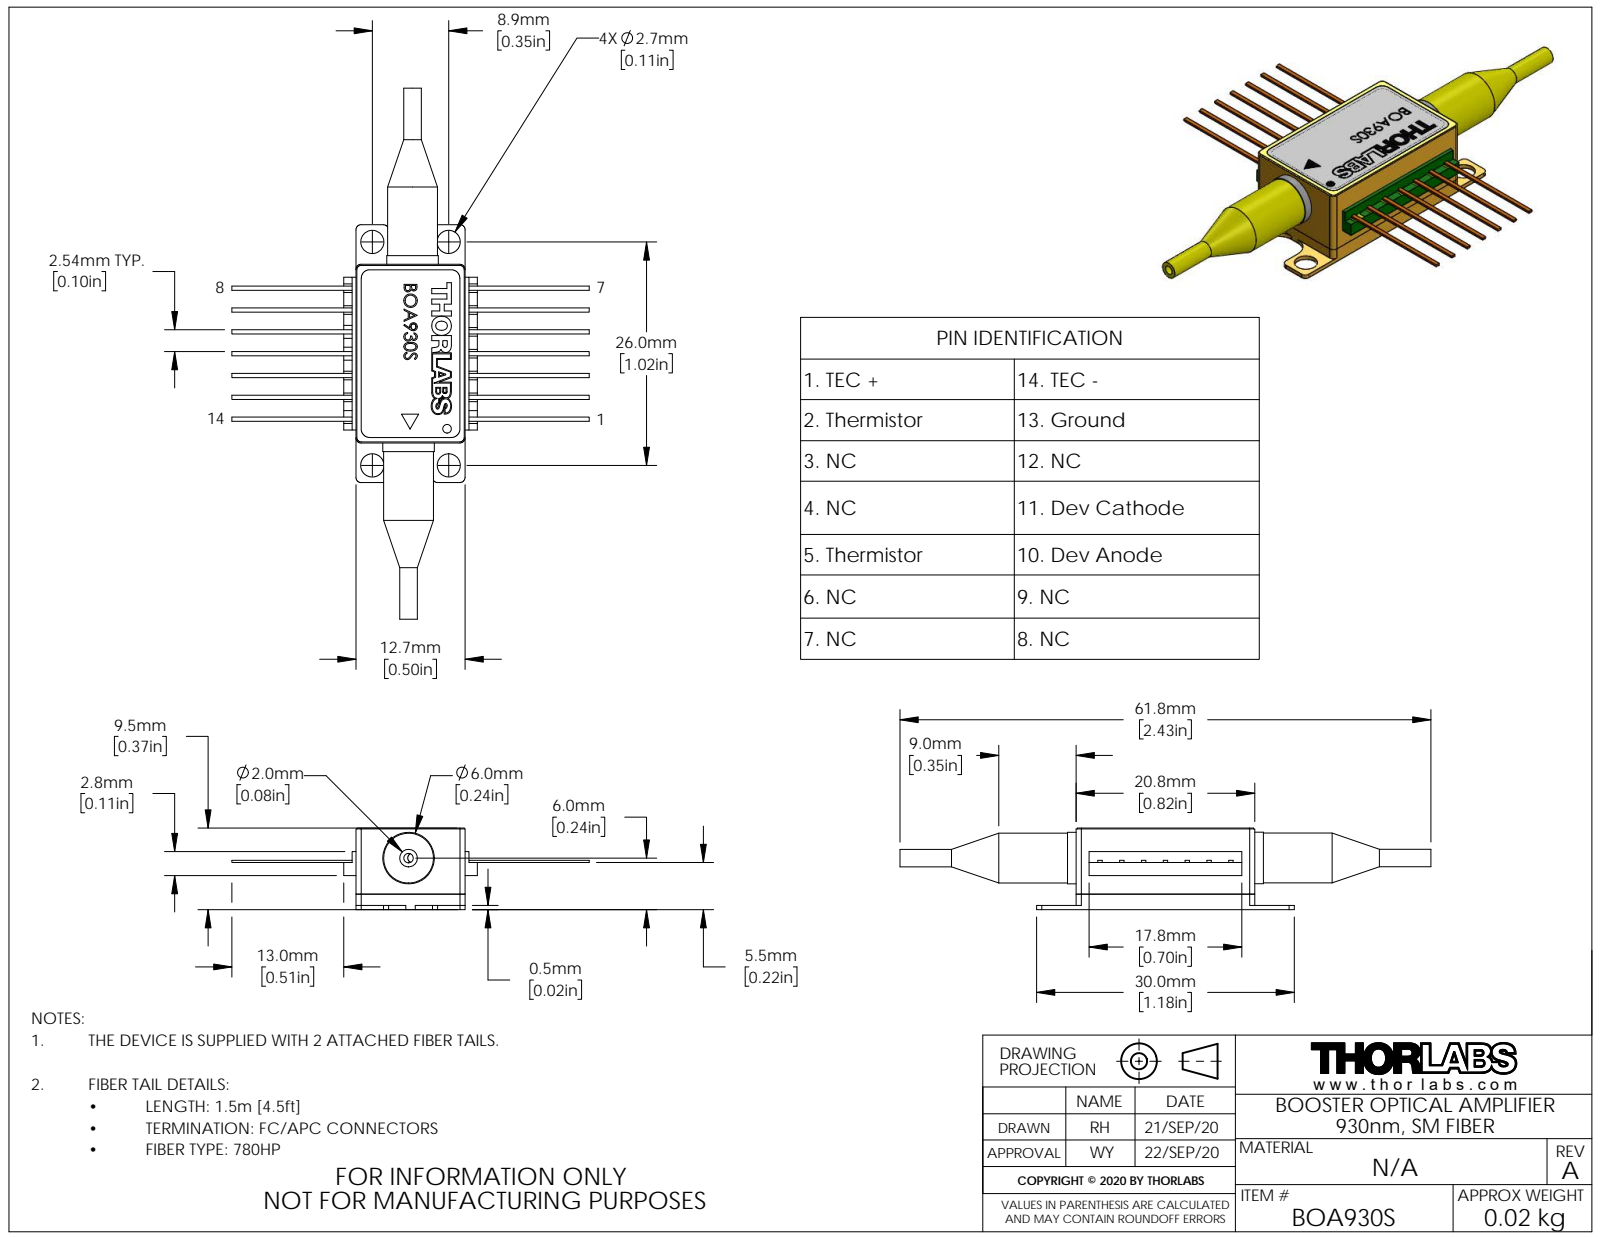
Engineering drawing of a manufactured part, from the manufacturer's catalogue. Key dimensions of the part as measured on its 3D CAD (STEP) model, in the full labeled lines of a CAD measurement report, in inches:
Part name (STEP PRODUCT): QTN039465-E0W
STEP written by: SolidWorks 2018 (AUTOMOTIVE_DESIGN)
Units: inches
Bodies: 0 solids, 344 faces (236 planar, 54 cylindrical, 54 other)
Overall size (bounding box): 2.433 × 1.638 × 0.374
Round holes (diameter × count): ⌀0.106 ×4, ⌀0.043 ×2, ⌀0.039 ×1
Round bosses / shafts (diameter × count): ⌀0.236 ×2, ⌀0.228 ×2, ⌀0.08 ×2
Partial cylindrical surfaces — rounded edges, fillets, slot ends (radius × count): R0.024 ×12, R0.02 ×4, R0.039 ×4, R0.079 ×4
Main face-to-face distances: 0.374, 0.5, 0.156, 0.217, 0.217, 0.06, 0.157, 0.02, 0.226, 0.07
Hole centre spacings: 0.35, 1.024, 1.082, 0.018, 0.168, 0.381, 0.856, 0.922
